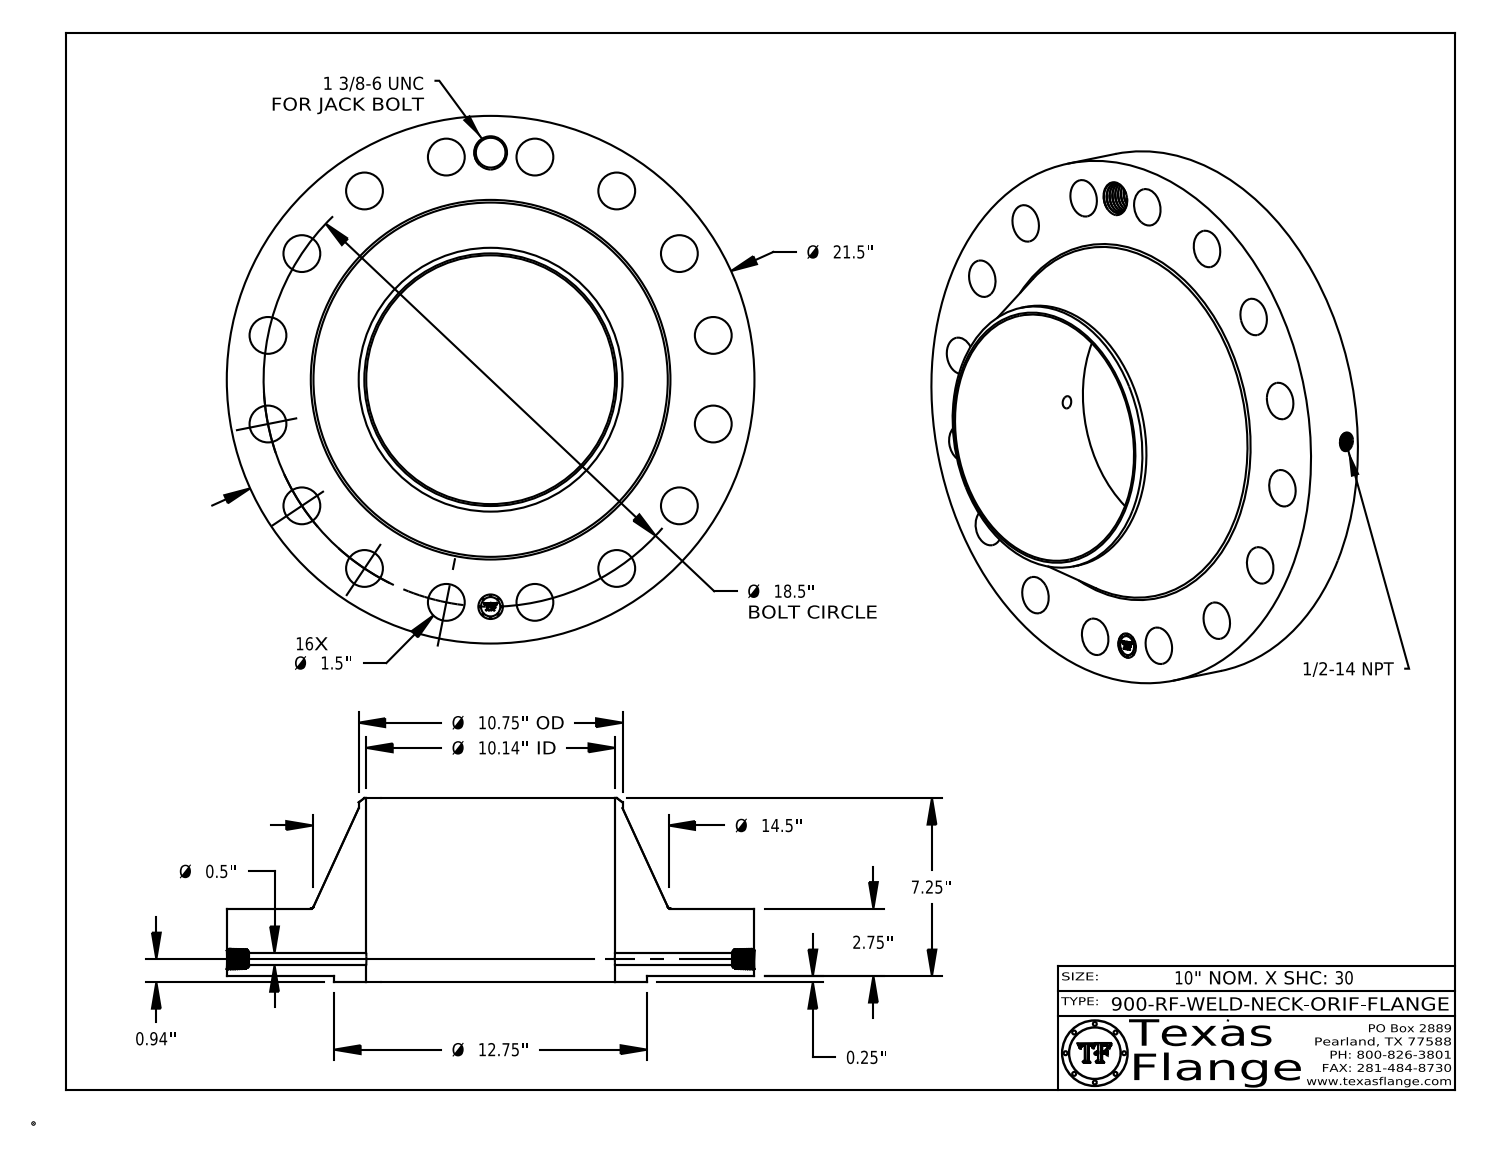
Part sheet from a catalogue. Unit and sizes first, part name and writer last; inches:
Units: inches
Overall size (bounding box): 21.5 × 21.5 × 7.5
Round holes (diameter × count): ⌀1.5 ×16, ⌀0.5 ×1, ⌀0.672 ×1, ⌀1 ×1, ⌀1.219 ×1, ⌀10.136 ×1
Round bosses / shafts (diameter × count): ⌀0.061 ×8, ⌀21.5 ×1, ⌀12.75 ×1, ⌀10.75 ×1, ⌀0.788 ×1
Main face-to-face distances: 2.75, 0.25, 3, 7.5, 7.25, 4.5, 2.985, 2.735, 0.015, 4.515
Hole centre spacings: 10.278, 17.092, 3.609, 9.25, 7.08, 7.08, 9.25, 13.081
Volume: 893.4 in³ · Surface area: 1 297 in²
Bodies: 1 solid, 794 faces (369 planar, 113 cylindrical, 312 other)
Part name (STEP PRODUCT): 900-RF-WELD-NECK
STEP written by: CATIA V5 STEP AP214 (AUTOMOTIVE_DESIGN)
